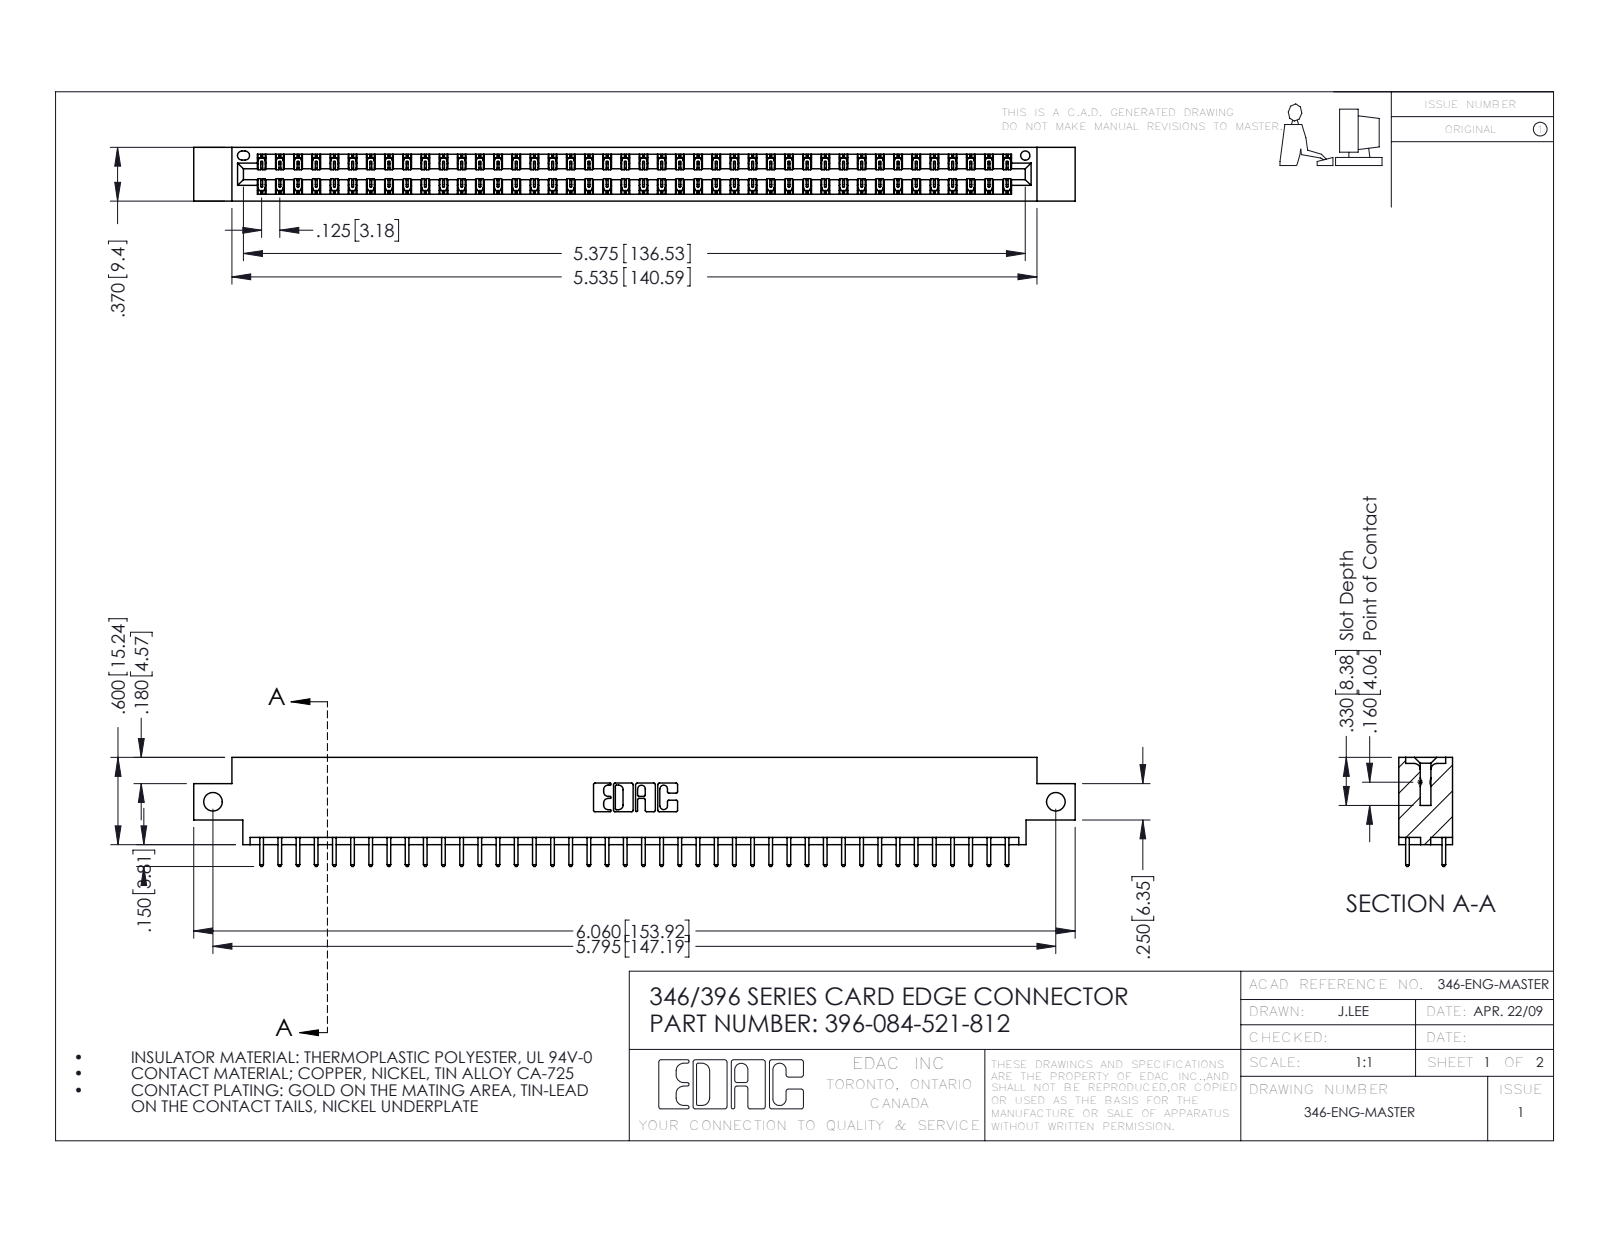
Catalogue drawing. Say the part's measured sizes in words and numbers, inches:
The part is named "345-292-001_345-293-121; 346 Part_0.170 Offset - Side Mount; 396-084-521-812". Its 3-D file was written by "SolidWorks 2016 (CONFIG_CONTROL_DESIGN)". It is 85 solids with 4494 faces: 3020 planar, 1474 cylindrical and 0 other. Overall it measures 6.06 by 0.75 by 0.37 inches. Its volume is 0.899 cubic inches and its surface area 31.1 square inches. Round holes: 2 of diameter 0.128, 1 of diameter 0.064. Partial cylindrical surfaces (rounded edges, fillets, slot ends): 126 of radius 0.006, 84 of radius 0.01, 22 of radius 0.01, 6 of radius 0.007, 6 of radius 0.031, 3 of radius 0.026, 2 of radius 0.014, 2 of radius 0.022. The main face-to-face distances are 0.048, 0.322, 0.37, 0.25, 0.072, 0.298, 0.025, 0.275, 0.148, 0.222. The hole center spacings are 5.795.
